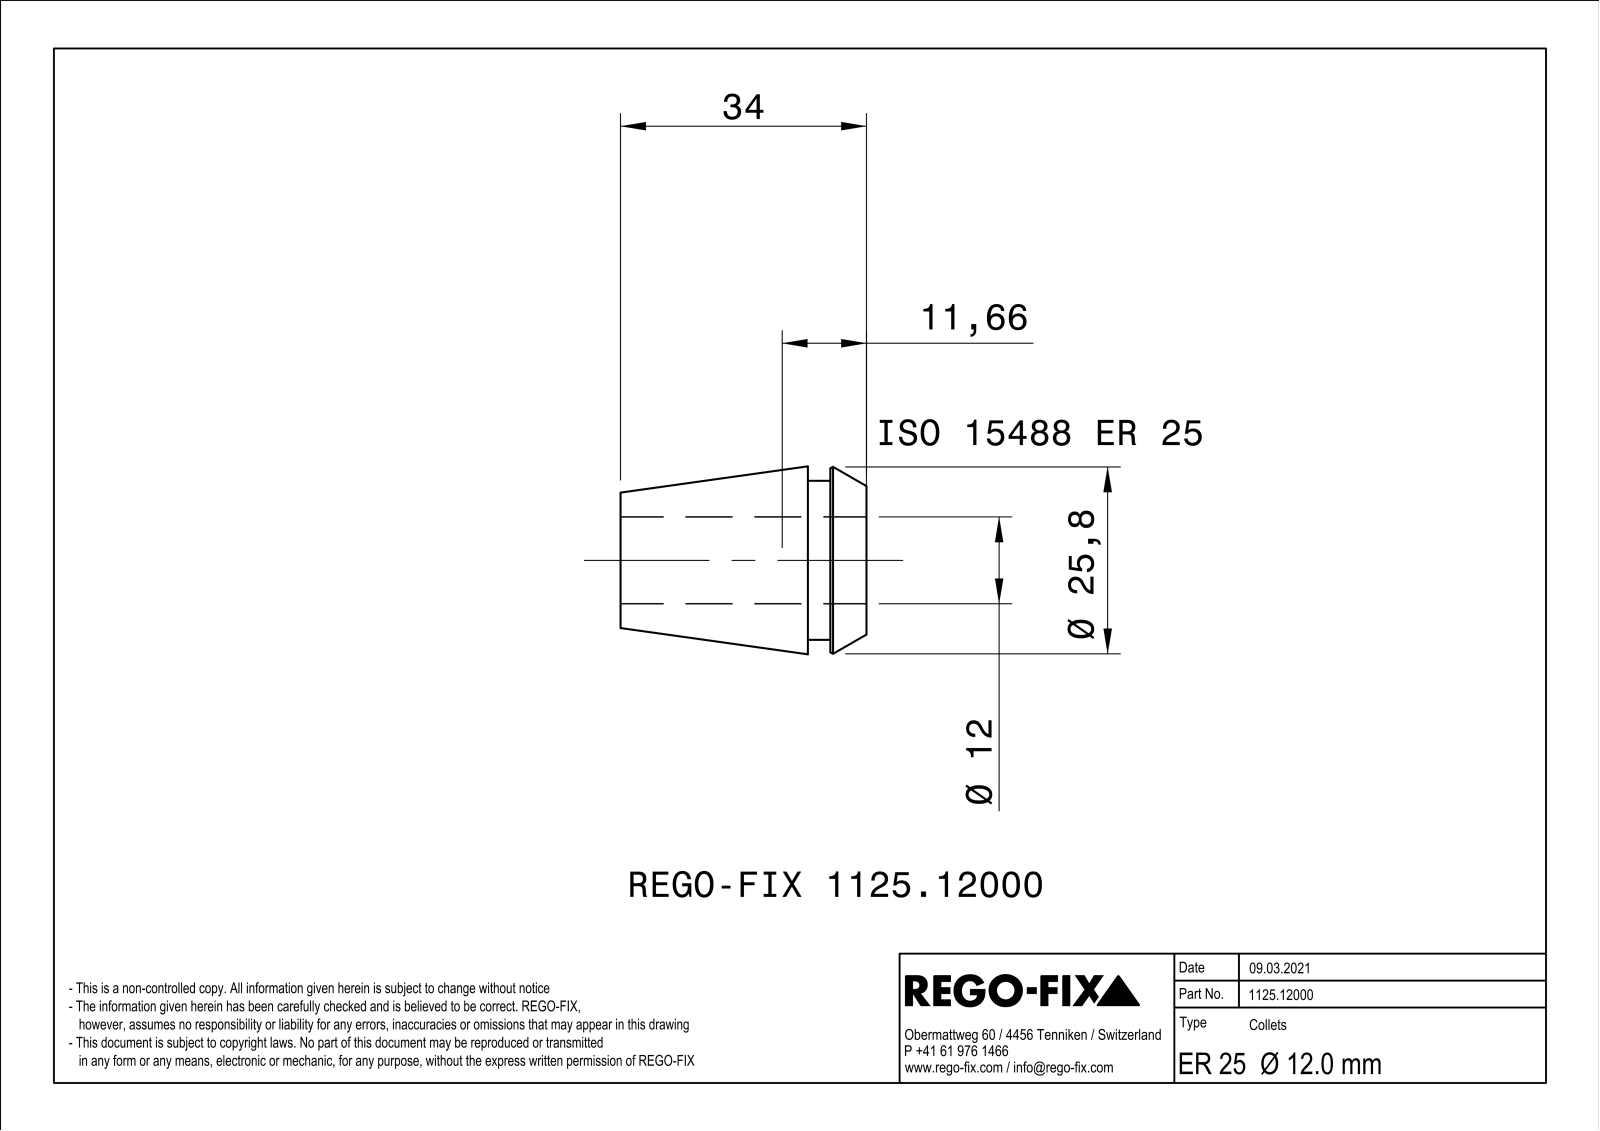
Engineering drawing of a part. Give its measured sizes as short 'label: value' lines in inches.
name: NOCUT
written by: SIEMENS PLM Software Solid Edge ST10 (AUTOMOTIVE_DESIGN)
unit: in
bodies: 1 solid, 177 faces (72 planar, 25 cylindrical, 80 other)
size: 1.339 × 1.023 × 1.023
volume: 0.472 in³; area: 13.35 in²
holes: 1× ⌀0.472
bosses: 1× ⌀0.866
rounds: 8× R0.016
face distances: 0.031, 1.339, 0.319, 1.02, 0.197, 0.122, 1.142
